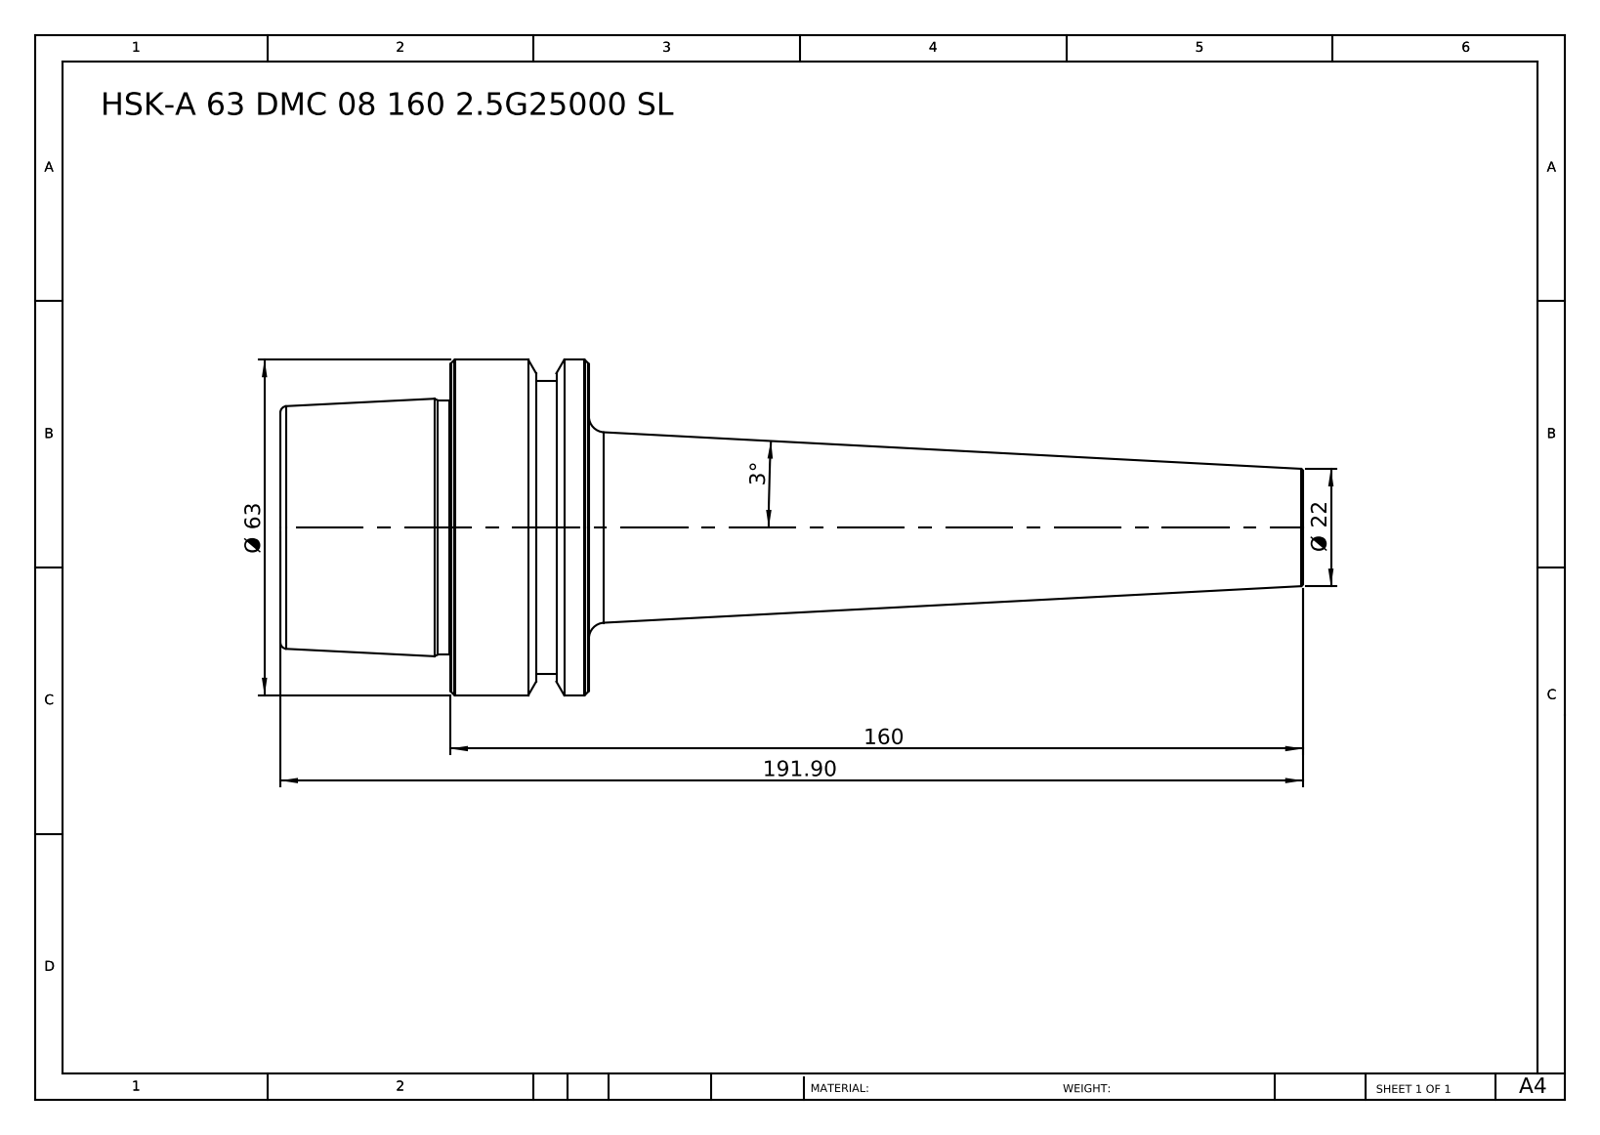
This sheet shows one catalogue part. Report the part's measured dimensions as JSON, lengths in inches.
{"part_name": "HSK-A 63 DMC 08 160 2.5G25000 SL", "step_written_by": "SolidWorks 2014 (CONFIG_CONTROL_DESIGN)", "units": "inches", "bodies": {"solids": 1, "faces": 46, "planar": 6, "cylindrical": 8, "other": 32}, "overall_size": [7.555, 2.48, 2.48], "volume_in3": 13.62, "surface_area_in2": 43.56, "round_bosses_or_shafts": [[2.48, 1], [2.165, 1], [1.881, 1]], "face_to_face_distances": [2.28, 1.024, 1.256, 5.276, 6.299, 7.555, 5.516, 0.24, 0.783, 2.039]}
